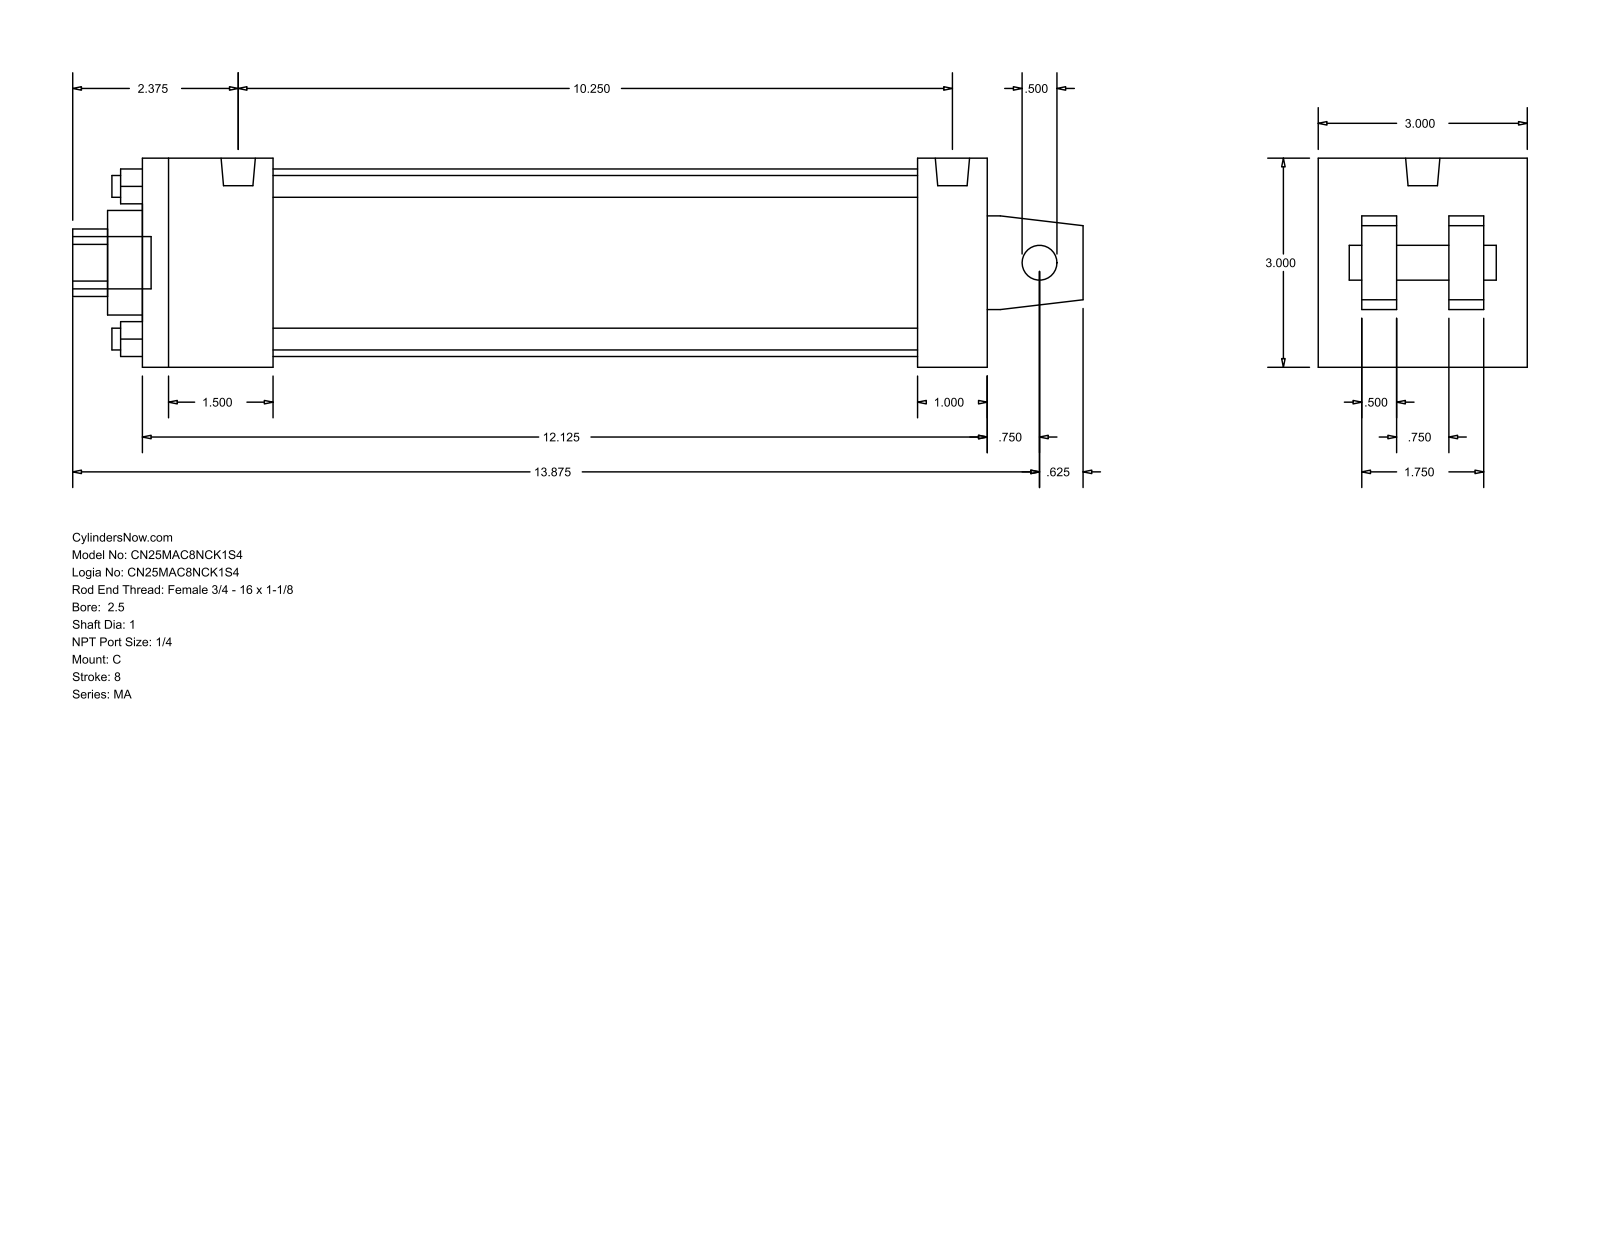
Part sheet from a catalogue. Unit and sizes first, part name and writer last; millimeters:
Units: millimetres
Overall size (bounding box): 368.3 × 76.2 × 76.2
Round holes (diameter × count): ⌀7.94 ×4, ⌀12.7 ×1, ⌀25.4 ×1, ⌀38.1 ×1, ⌀68.33 ×1
Round bosses / shafts (diameter × count): ⌀7.94 ×4, ⌀12.49 ×2, ⌀19.05 ×1
Partial cylindrical surfaces — rounded edges, fillets, slot ends (radius × count): R12.29 ×1
Main face-to-face distances: 76.2, 307.98, 47.63, 12.7, 15.87, 60.33, 25.4, 28.57, 282.58, 234.95
Hole centre spacings: 39.33, 55.62, 78.66
Bodies: 0 solids, 103 faces (76 planar, 27 cylindrical, 0 other)
Part name (STEP PRODUCT): MA_C__0250_1
STEP written by: GSSL Pune (CONFIG_CONTROL_DESIGN)
